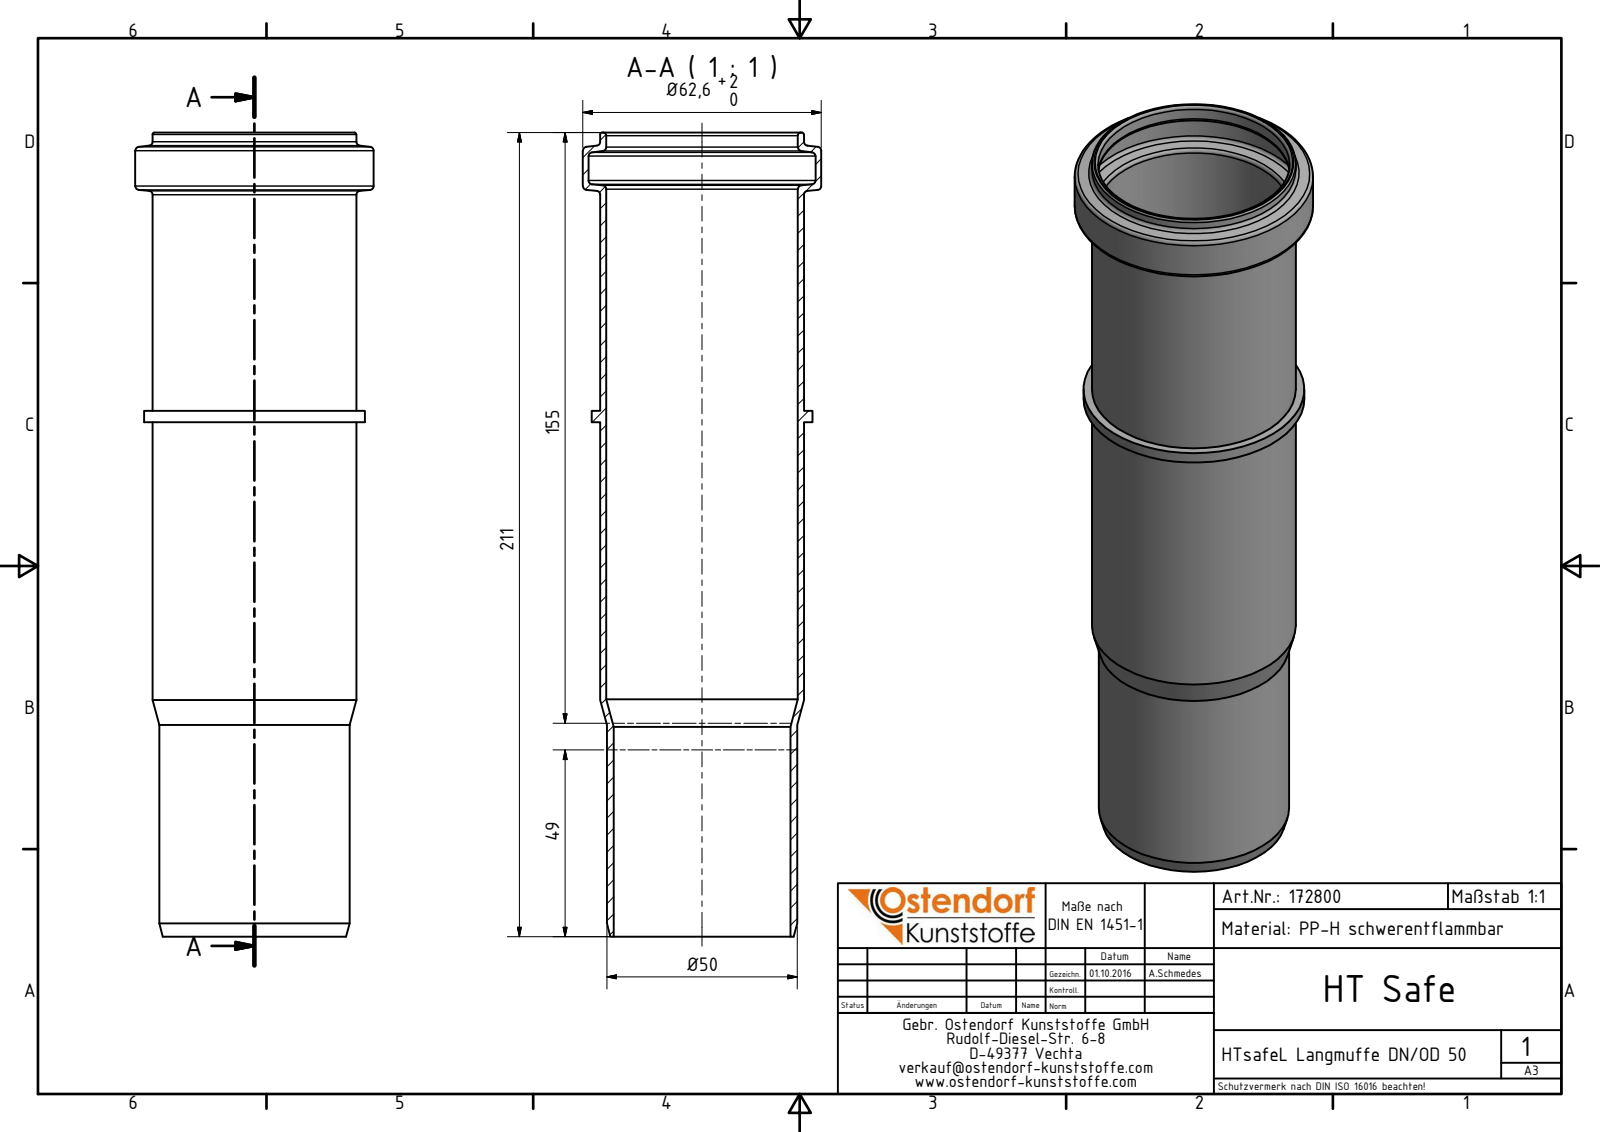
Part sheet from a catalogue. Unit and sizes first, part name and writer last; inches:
Units: inches
Overall size (bounding box): 8.307 × 2.465 × 2.465
Round holes (diameter × count): ⌀1.827 ×1, ⌀1.98 ×1, ⌀2.346 ×1
Round bosses / shafts (diameter × count): ⌀2.465 ×1, ⌀2.283 ×1, ⌀2.106 ×1, ⌀1.969 ×1
Main face-to-face distances: 0.118, 5.315, 5.433, 8.307, 2.992, 2.874
Volume: 3.614 in³ · Surface area: 111.1 in²
Bodies: 1 solid, 31 faces (4 planar, 10 cylindrical, 17 other)
Part name (STEP PRODUCT): 172800 HTsafeL DN_OD 50
STEP written by: Autodesk Inventor 2016 (AUTOMOTIVE_DESIGN)
